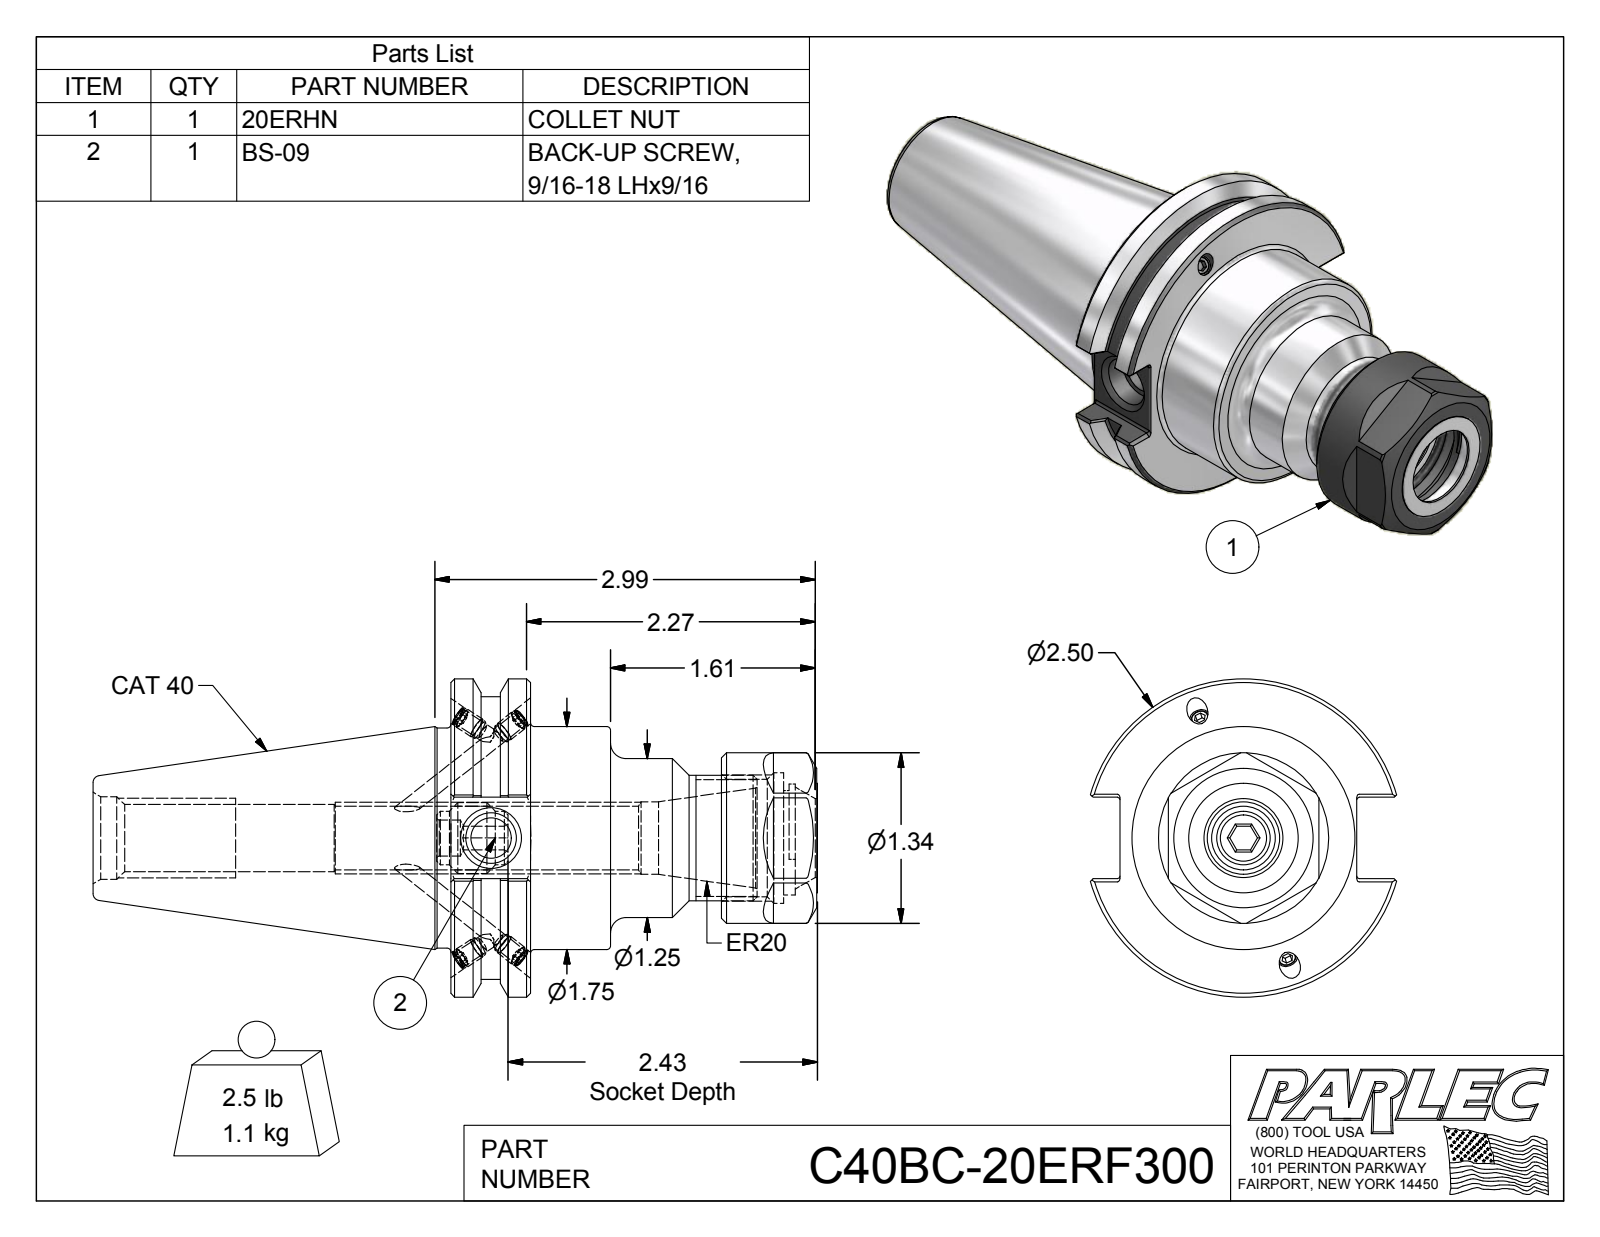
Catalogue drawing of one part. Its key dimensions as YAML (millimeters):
part_name: "C40BCB-20ER3-1; 029-965; BS-09; 20ERHN (+1 more)"
step_written_by: "Autodesk Inventor 2016 (AUTOMOTIVE_DESIGN)"
units: millimeters
bodies: {solids: 7, faces: 232, planar: 107, cylindrical: 59, other: 66}
overall_size: [144.45, 63.5, 61.11]
volume: 145551
surface_area: 33297
round_holes:
  - {diameter: 3.3, count: 4}
  - {diameter: 4.1, count: 4}
  - {diameter: 7.14, count: 1}
  - {diameter: 8, count: 1}
  - {diameter: 10.13, count: 1}
  - {diameter: 12.75, count: 1}
  - {diameter: 13.39, count: 1}
  - {diameter: 14.48, count: 1}
  - {diameter: 15.49, count: 1}
  - {diameter: 16.46, count: 1}
  - {diameter: 23.5, count: 1}
  - {diameter: 26, count: 1}
round_bosses_or_shafts:
  - {diameter: 4.2, count: 4}
  - {diameter: 4, count: 4}
  - {diameter: 63.5, count: 1}
  - {diameter: 56.36, count: 1}
  - {diameter: 44.45, count: 1}
  - {diameter: 43.94, count: 1}
  - {diameter: 34, count: 1}
  - {diameter: 31.75, count: 1}
partial_cylinders:
  - {radius: 0.51, count: 12}
  - {radius: 9.47, count: 1}
  - {radius: 10.55, count: 1}
  - {radius: 10.75, count: 1}
face_to_face_distances: [15.88, 73.03, 57.15, 30, 31.88, 16, 41.15, 53.96, 38.08, 22.08]
